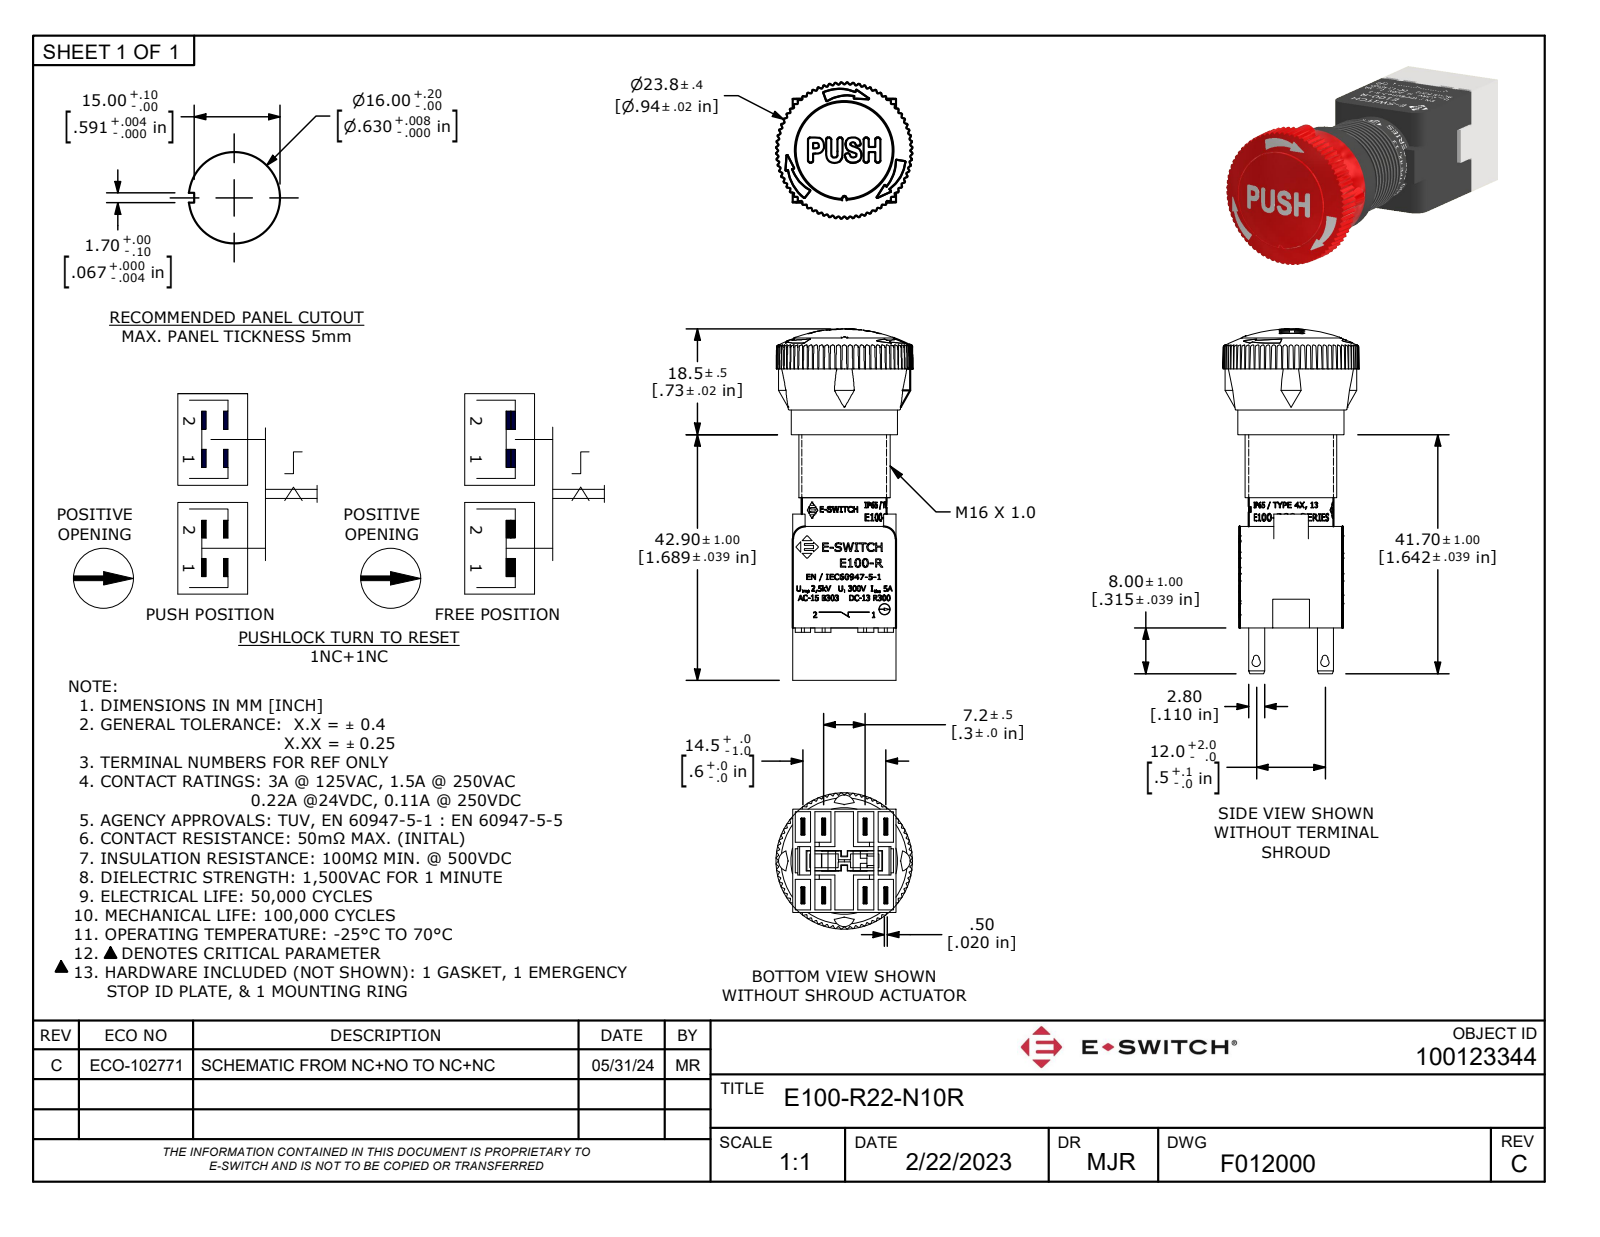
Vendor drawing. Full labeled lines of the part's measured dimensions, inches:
Part name (STEP PRODUCT): E100-R22-N10R
STEP written by: Autodesk Inventor 2022 (AUTOMOTIVE_DESIGN)
Units: inches
Bodies: 1 solid, 3824 faces (2206 planar, 197 cylindrical, 1421 other)
Overall size (bounding box): 2.417 × 0.936 × 0.936
Volume: 0.941 in³ · Surface area: 15.25 in²
Round holes (diameter × count): ⌀0.071 ×2, ⌀0.677 ×1, ⌀0.728 ×1
Round bosses / shafts (diameter × count): ⌀0.079 ×2, ⌀0.73 ×1, ⌀0.669 ×1, ⌀0.63 ×1, ⌀0.583 ×1
Partial cylindrical surfaces — rounded edges, fillets, slot ends (radius × count): R0.004 ×72, R0.004 ×16, R0.071 ×4, R0.02 ×3, R0.03 ×3, R0.085 ×2, R7.839 ×2, R0.008 ×1
Main face-to-face distances: 0.709, 0.02, 0.018, 0.691, 0.266, 0.138, 0.283, 0.404, 0.121, 0.587
Hole centre spacings: 0.554
